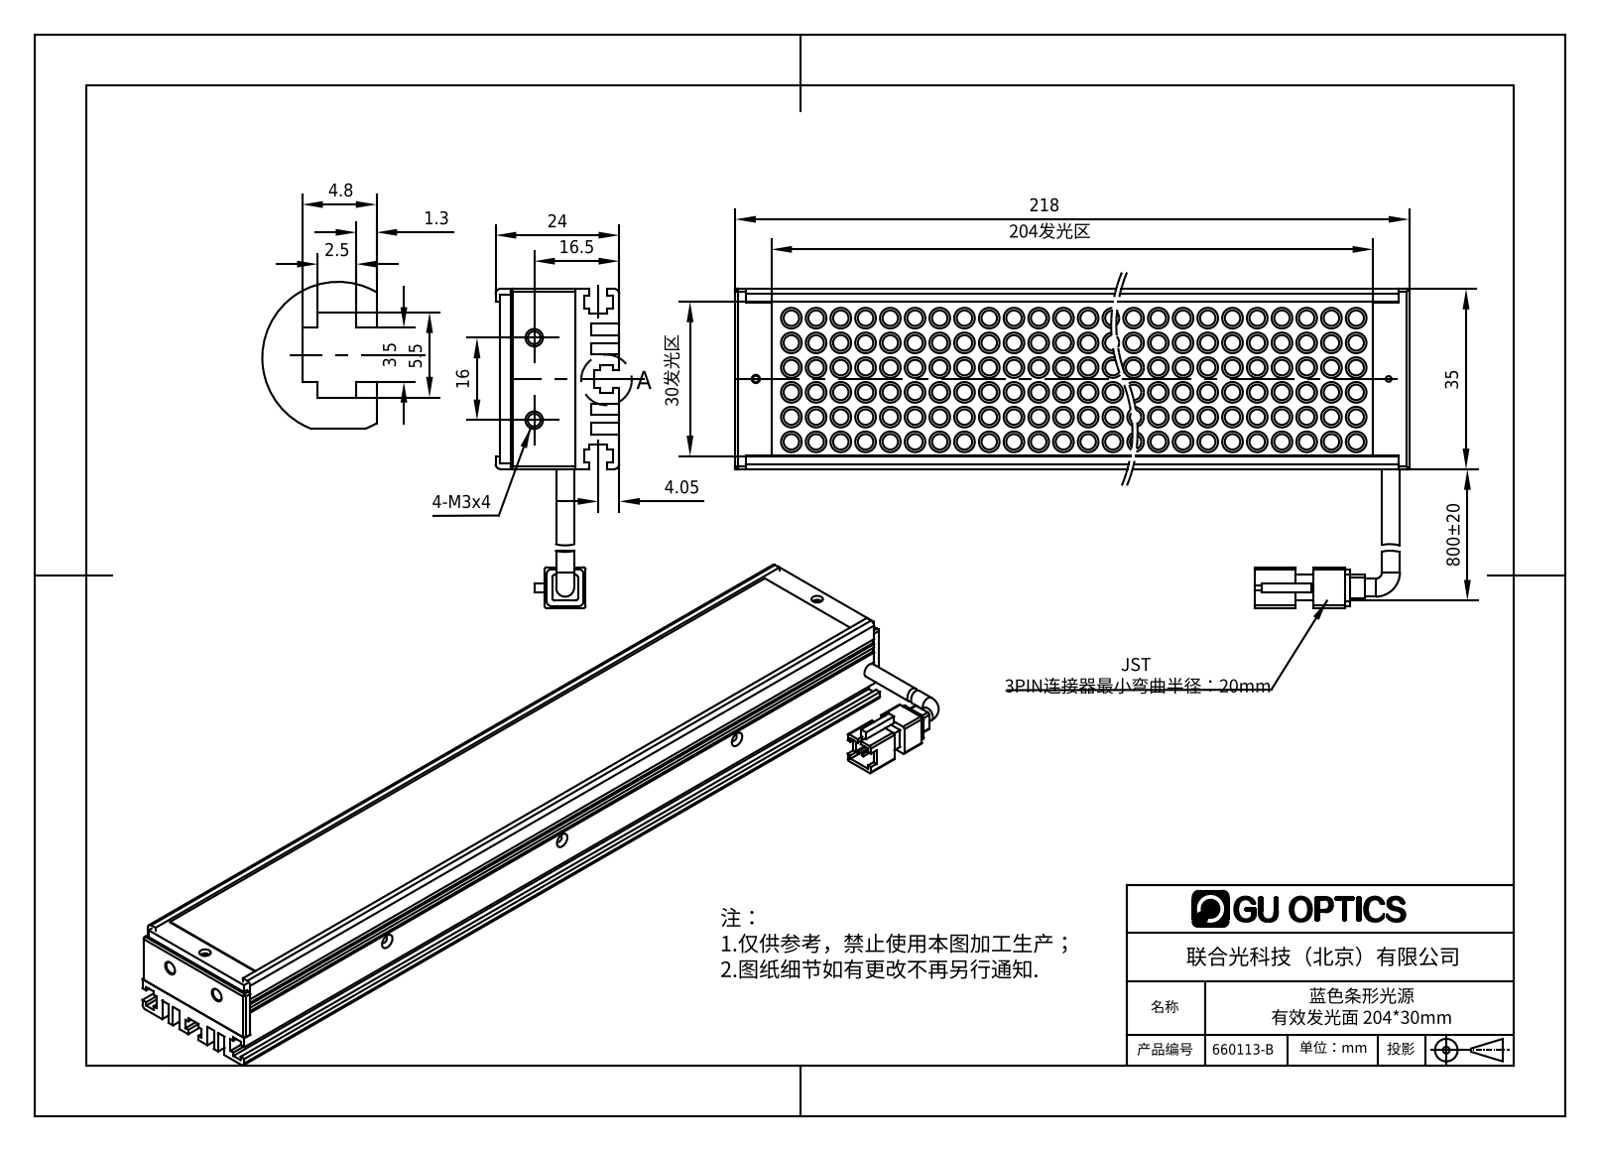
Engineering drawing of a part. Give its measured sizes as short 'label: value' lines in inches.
name: 660113-B
written by: SolidWorks 2016 (AUTOMOTIVE_DESIGN)
unit: in
bodies: 8 solids, 1974 faces (520 planar, 1095 cylindrical, 359 other)
size: 8.583 × 2.441 × 0.945
volume: 5.935 in³; area: 171.8 in²
holes: 5× ⌀0.063, 3× ⌀0.067, 2× ⌀0.059, 2× ⌀0.098, 2× ⌀0.11, 2× ⌀0.118, 1× ⌀0.043, 1× ⌀0.049, 1× ⌀0.079
bosses: 252× ⌀0.157, 252× ⌀0.118, 2× ⌀0.138
rounds: 12× R0.039, 8× R0.02, 1× R0.065
face distances: 0.079, 0.087, 0.339, 0.039, 0.098, 0.354, 0.157, 0.496, 0.575, 0.417
hole spacings: 8.268, 0.276, 1.773, 1.784, 2.362, 4.134, 4.139, 6.496
